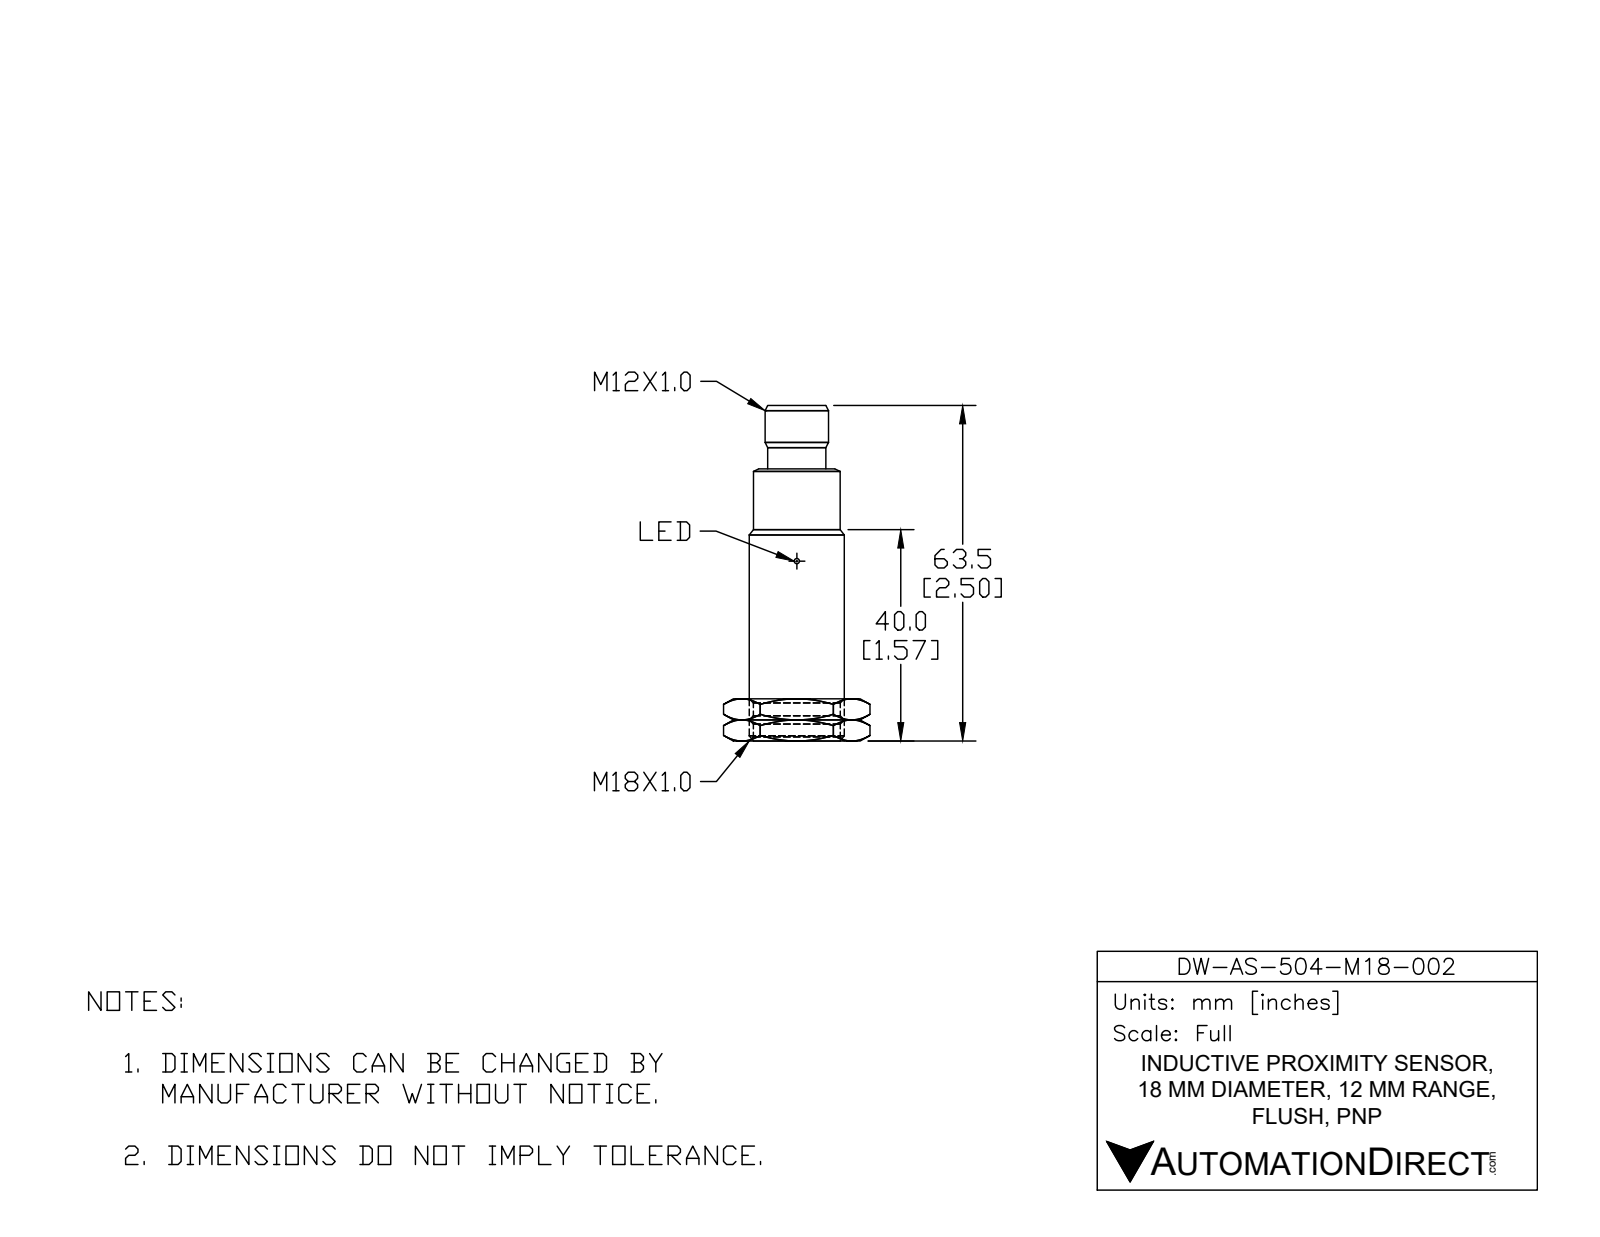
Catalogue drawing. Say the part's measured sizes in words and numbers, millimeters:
The part is named "DW-AS-504-M18-002". Its 3-D file was written by "SolidWorks 2017 (AUTOMOTIVE_DESIGN)". It is 1 solid with 38 faces: 8 planar, 20 cylindrical and 10 other. Overall it measures 63.6 by 18 by 18 millimeters. Its volume is 13 300 cubic millimeters and its surface area 4 126 square millimeters. Round holes: 2 of diameter 3, 1 of diameter 8.5. Round bosses or shafts: 4 of diameter 1, 1 of diameter 18, 1 of diameter 16.4, 1 of diameter 12, 1 of diameter 10.5. Partial cylindrical surfaces (rounded edges, fillets, slot ends): 2 of radius 0.6, 1 of radius 4.9. The main face-to-face distances are 50.5, 54.9, 4.4, 63.6, 13.1, 8.7, 1.1, 41.5, 9, 13.4.
